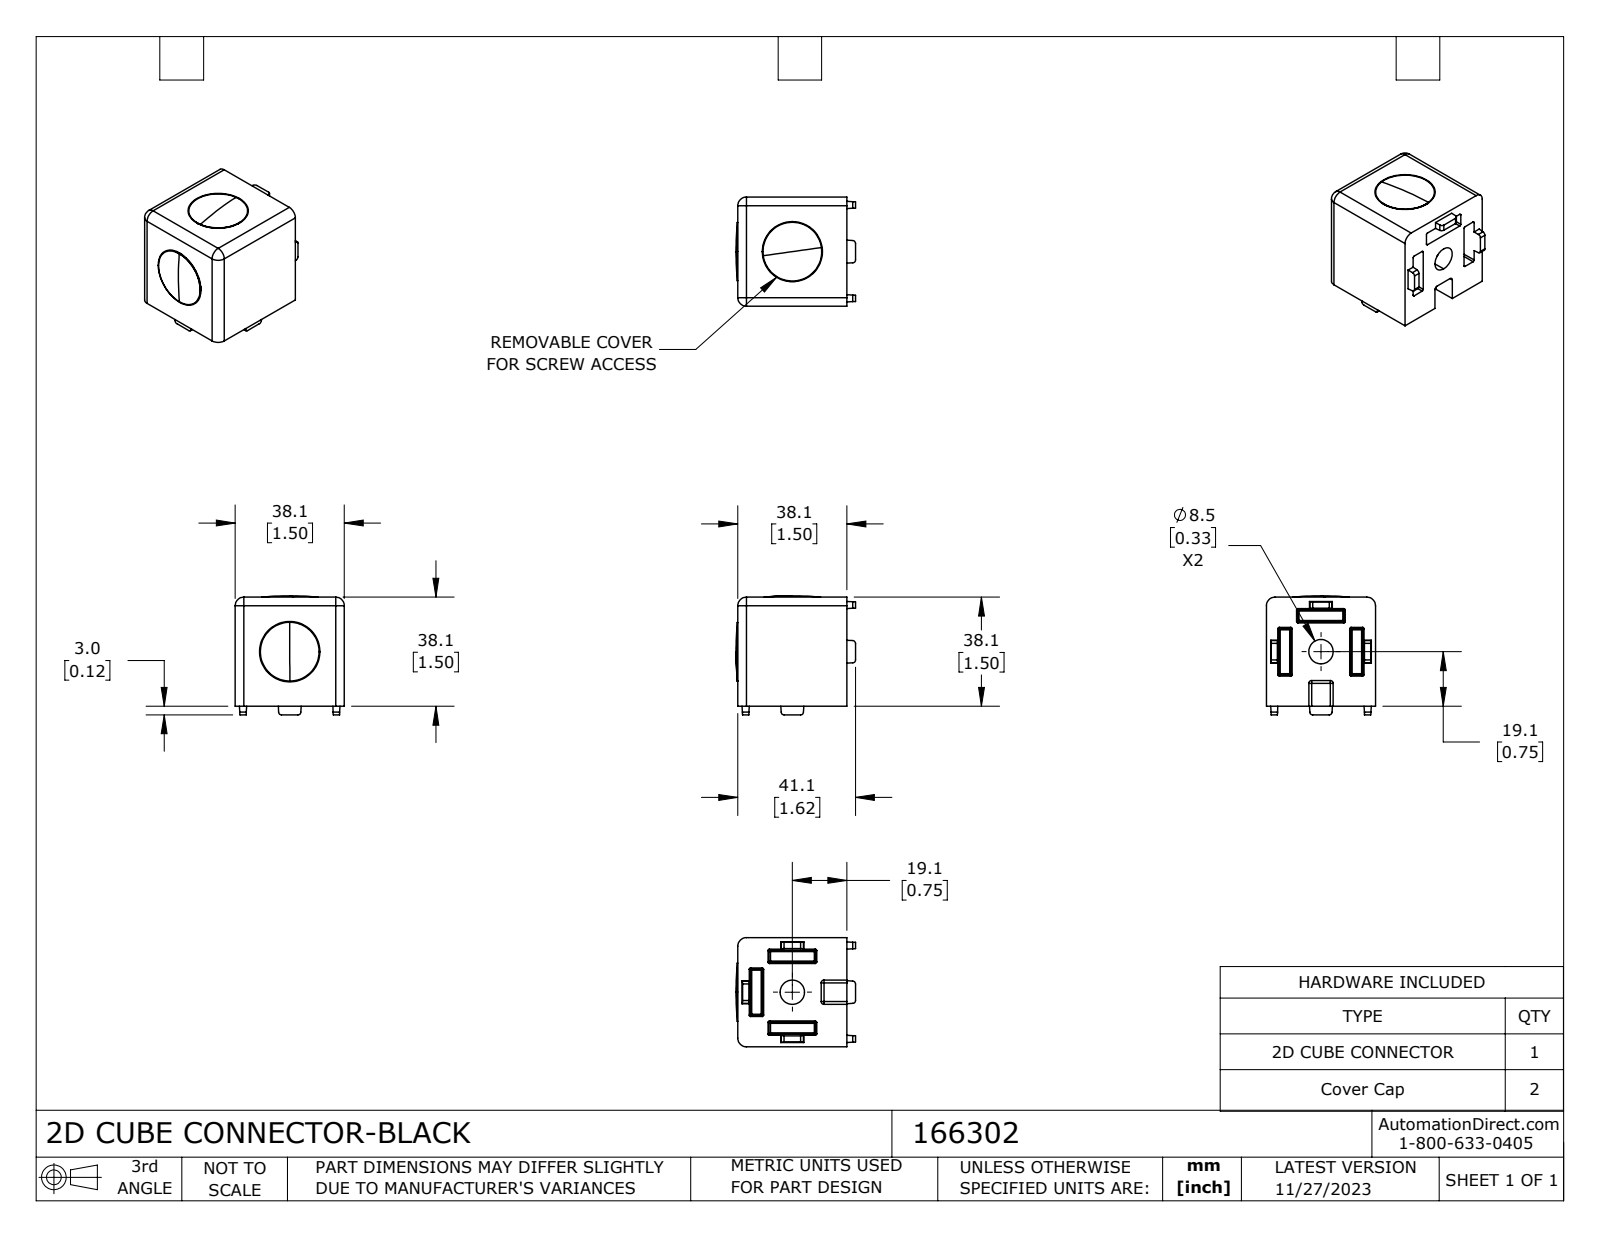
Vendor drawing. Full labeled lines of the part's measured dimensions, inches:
Part name (STEP PRODUCT): 166302
STEP written by: SolidWorks 2023 (CONFIG_CONTROL_DESIGN)
Units: inches
Bodies: 3 solids, 250 faces (84 planar, 92 cylindrical, 74 other)
Overall size (bounding box): 1.643 × 1.636 × 1.5
Volume: 2.442 in³ · Surface area: 23.54 in²
Round holes (diameter × count): ⌀0.335 ×2
Round bosses / shafts (diameter × count): ⌀0.661 ×2
Partial cylindrical surfaces — rounded edges, fillets, slot ends (radius × count): R0.02 ×44, R0.039 ×13, R0.071 ×12, R0.118 ×5
Main face-to-face distances: 1.5, 0.987, 0.039, 0.276, 1.224, 0.236, 1.264, 0.015, 1.485, 1.479
